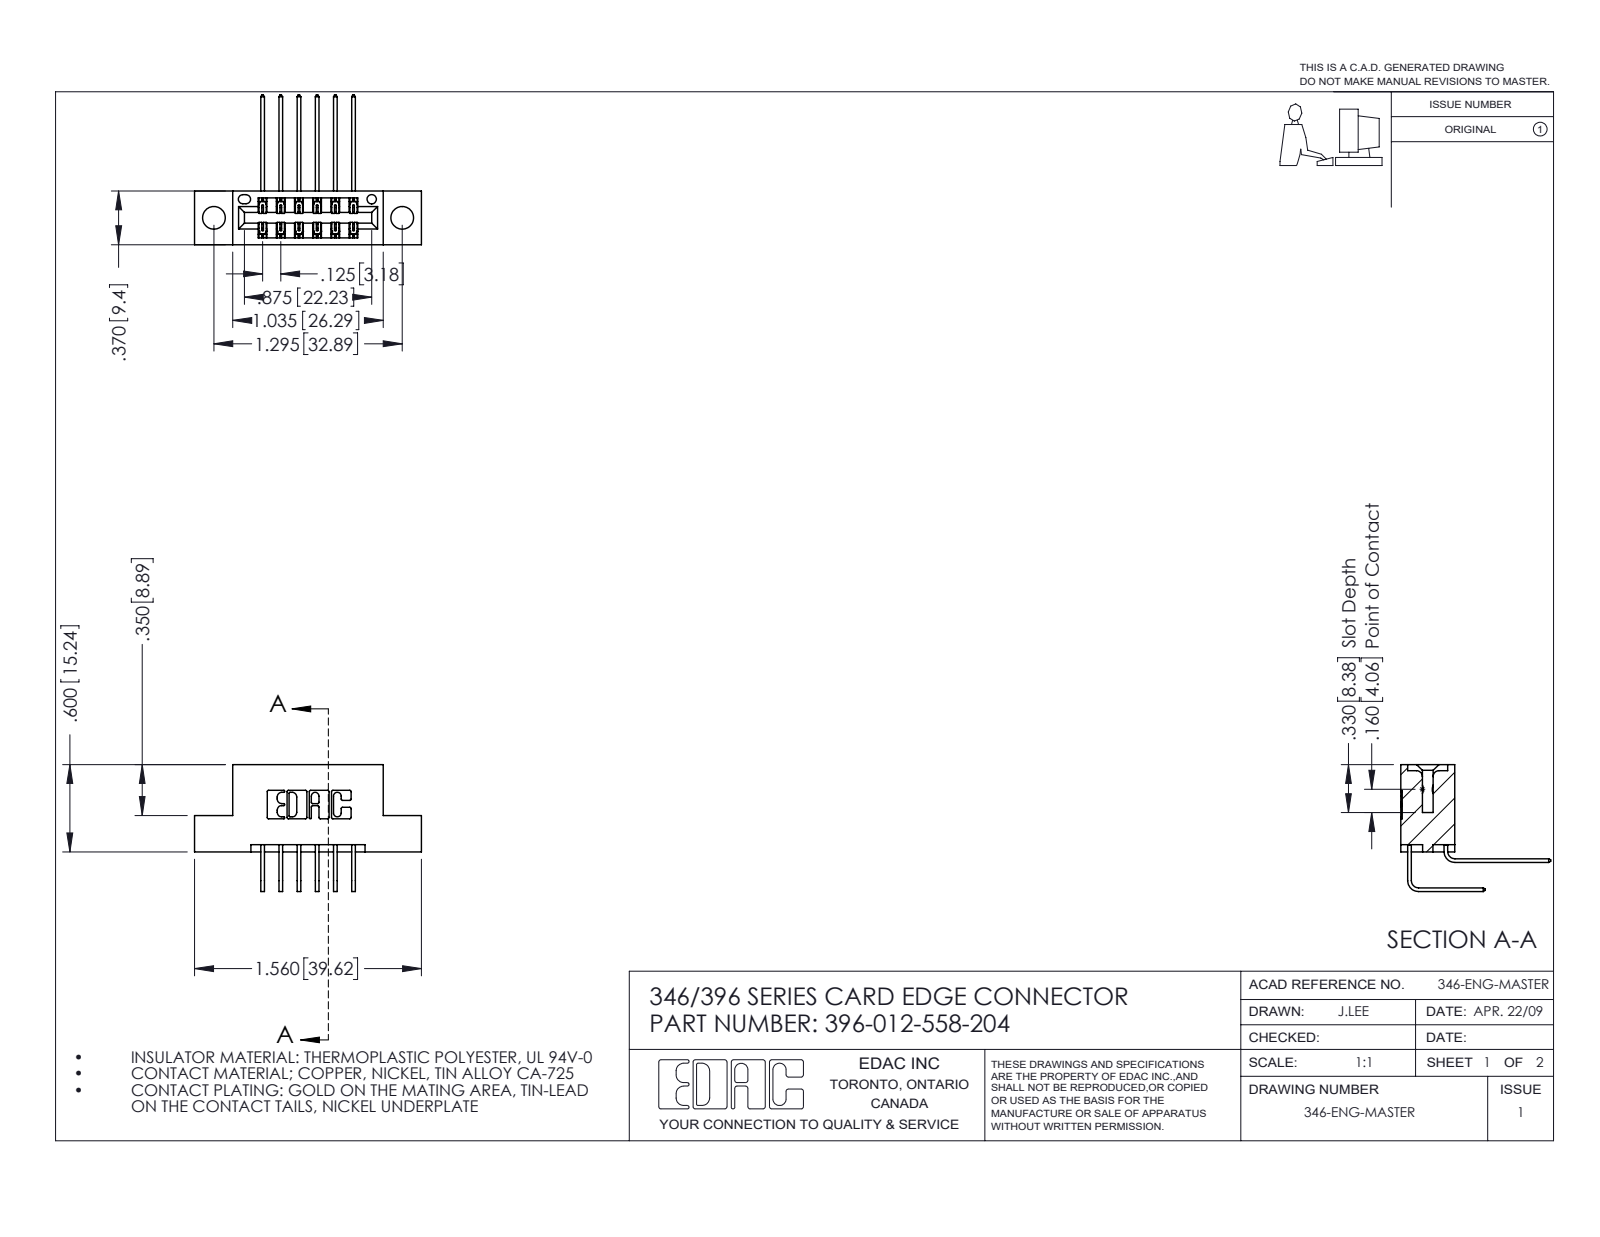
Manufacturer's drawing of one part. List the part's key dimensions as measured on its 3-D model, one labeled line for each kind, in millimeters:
Part name (STEP PRODUCT): 346 Part_Flush Mounting Lugs - 0.156 Dia-TH; 345-292-001_558 559 Tail - 1; 345-292-001_558 Tail - 2; 396-012-558-204
STEP written by: SolidWorks 2016 (CONFIG_CONTROL_DESIGN)
Units: millimetres
Bodies: 13 solids, 770 faces (520 planar, 250 cylindrical, 0 other)
Overall size (bounding box): 39.6 × 26.2 × 22.2
Volume: 3 570 mm³ · Surface area: 4 481 mm²
Round holes (diameter × count): ⌀4 ×2, ⌀1.6 ×1
Partial cylindrical surfaces — rounded edges, fillets, slot ends (radius × count): R0.3 ×22, R0.2 ×18, R0.2 ×6, R0.8 ×6, R0.7 ×3, R0.4 ×2, R0.6 ×2, R0.6 ×2
Main face-to-face distances: 6.4, 8.2, 1.2, 9.4, 7.6, 0.6, 1.8, 3.2, 3.8, 5.6
Hole centre spacings: 6.2, 27.7, 32.9
